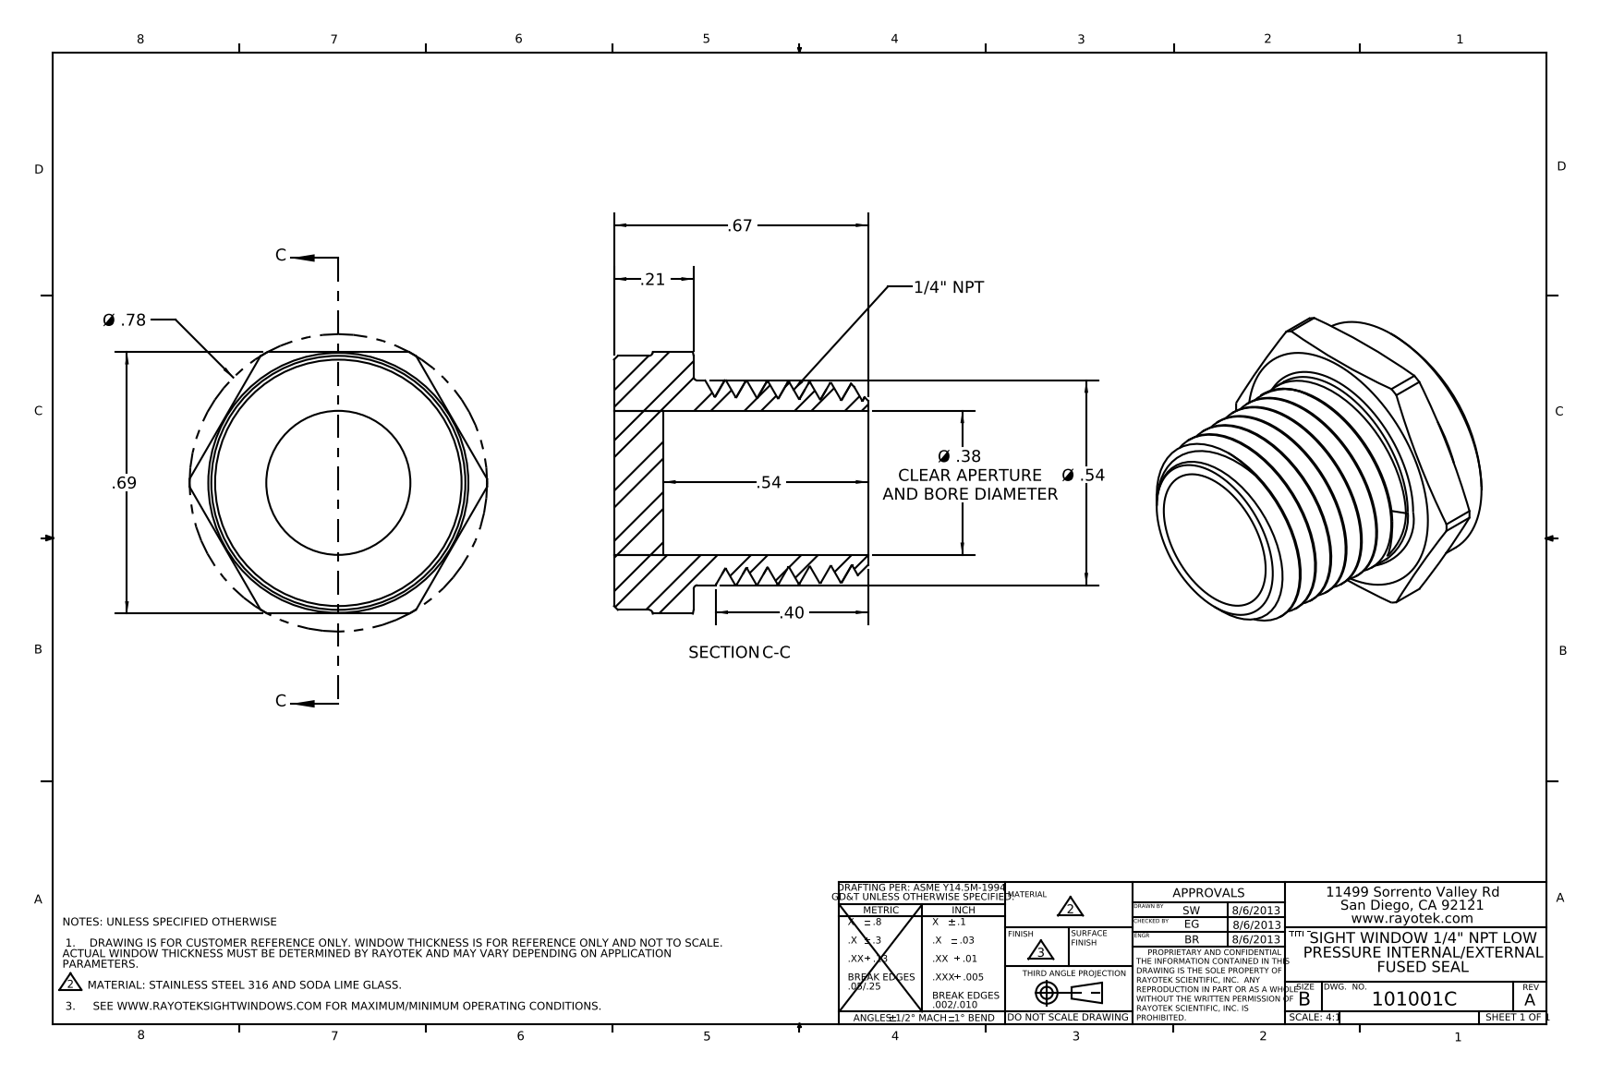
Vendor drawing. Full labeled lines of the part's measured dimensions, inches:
Part name (STEP PRODUCT): 403001
STEP written by: SolidWorks 2012 (AUTOMOTIVE_DESIGN)
Units: inches
Bodies: 2 solids, 59 faces (14 planar, 16 cylindrical, 29 other)
Overall size (bounding box): 0.785 × 0.69 × 0.67
Volume: 0.107 in³ · Surface area: 3.392 in²
Round holes (diameter × count): ⌀0.38 ×1
Round bosses / shafts (diameter × count): ⌀0.67 ×1, ⌀0.54 ×1
Partial cylindrical surfaces — rounded edges, fillets, slot ends (radius × count): R0.392 ×1
Main face-to-face distances: 0.13, 0.69, 0.21, 0.08, 0.67, 0.54, 0.46
